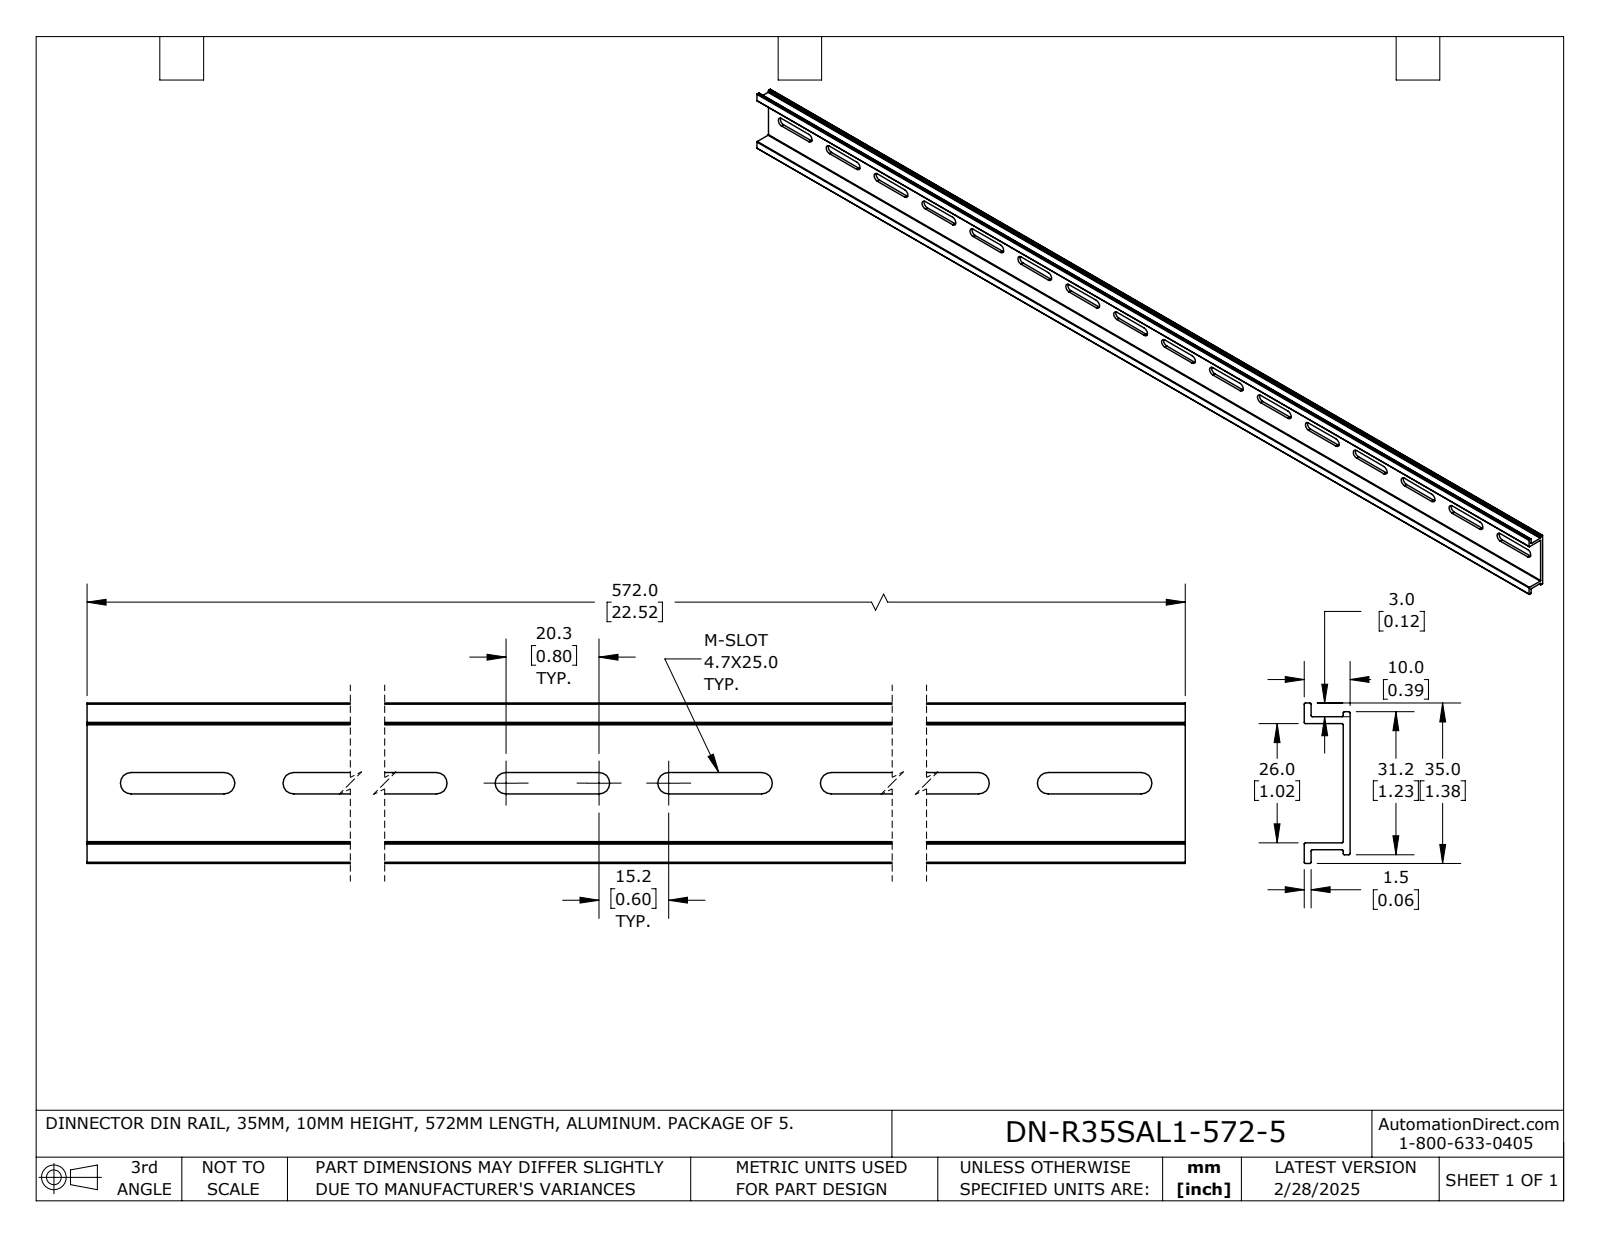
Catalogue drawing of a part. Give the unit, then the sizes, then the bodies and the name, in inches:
Units: inches
Overall size (bounding box): 22.52 × 1.378 × 0.394
Partial cylindrical surfaces — rounded edges, fillets, slot ends (radius × count): R0.093 ×32, R0.011 ×16
Main face-to-face distances: 0.059, 1.083, 0.335, 1.024, 0.394, 1.142, 0.276, 0.043, 0.102, 1.126
Volume: 2.671 in³ · Surface area: 93.85 in²
Bodies: 1 solid, 98 faces (50 planar, 48 cylindrical, 0 other)
Part name (STEP PRODUCT): DN-R35SAL1-572-5_Default
STEP written by: SolidWorks 2024 (CONFIG_CONTROL_DESIGN)
